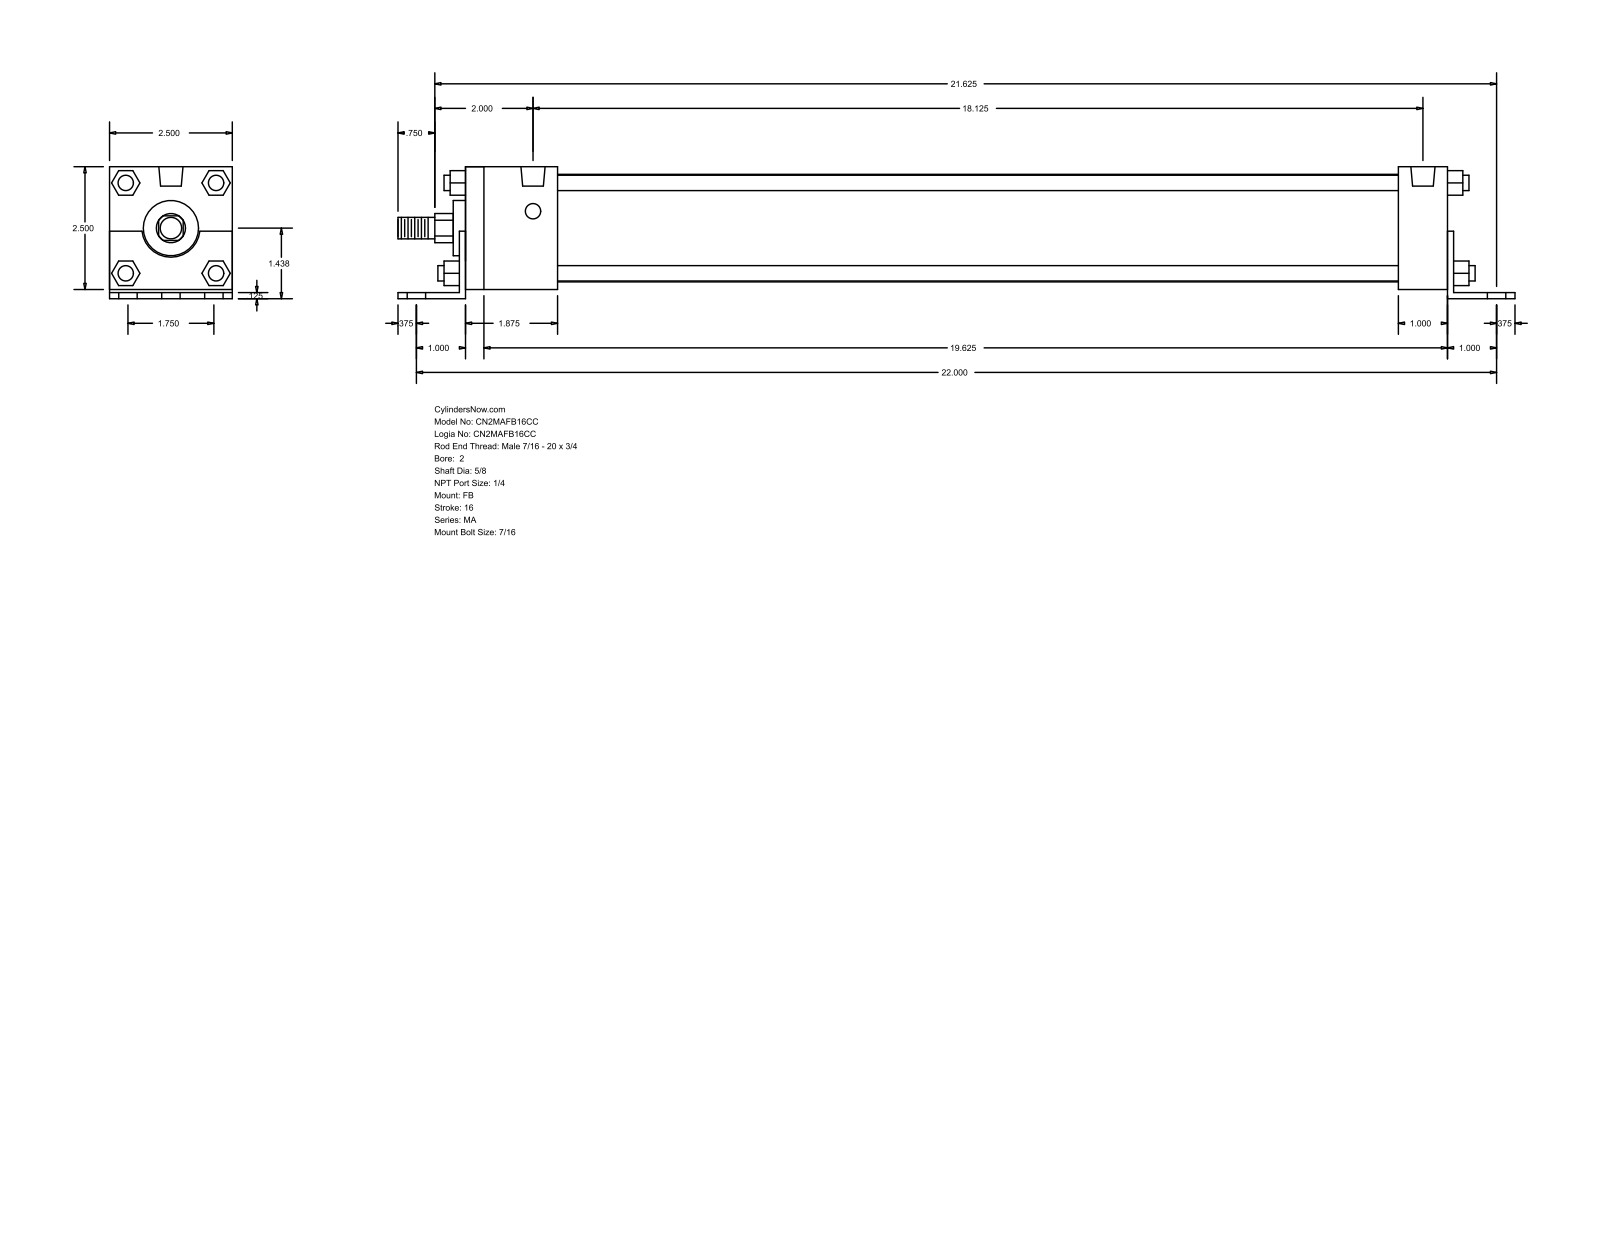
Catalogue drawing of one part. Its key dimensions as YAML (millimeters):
part_name: "MA_FB__0200_0.625"
step_written_by: "GSSL Pune (CONFIG_CONTROL_DESIGN)"
units: millimeters
bodies: {solids: 0, faces: 140, planar: 105, cylindrical: 35, other: 0}
overall_size: [577.85, 68.26, 63.5]
round_holes:
  - {diameter: 11.11, count: 6}
  - {diameter: 7.94, count: 4}
  - {diameter: 12.49, count: 2}
round_bosses_or_shafts:
  - {diameter: 7.94, count: 4}
  - {diameter: 55.63, count: 1}
  - {diameter: 28.57, count: 1}
  - {diameter: 15.88, count: 1}
  - {diameter: 11.11, count: 1}
partial_cylinders:
  - {radius: 7.54, count: 1}
  - {radius: 15.05, count: 1}
face_to_face_distances: [63.5, 3.17, 4.76, 68.26, 1.59, 65.09, 514.35, 3.18, 508, 511.17]
hole_center_spacings: [22.23, 559.24, 558.8, 44.1, 44.46, 64.3, 460.38, 498.97]
